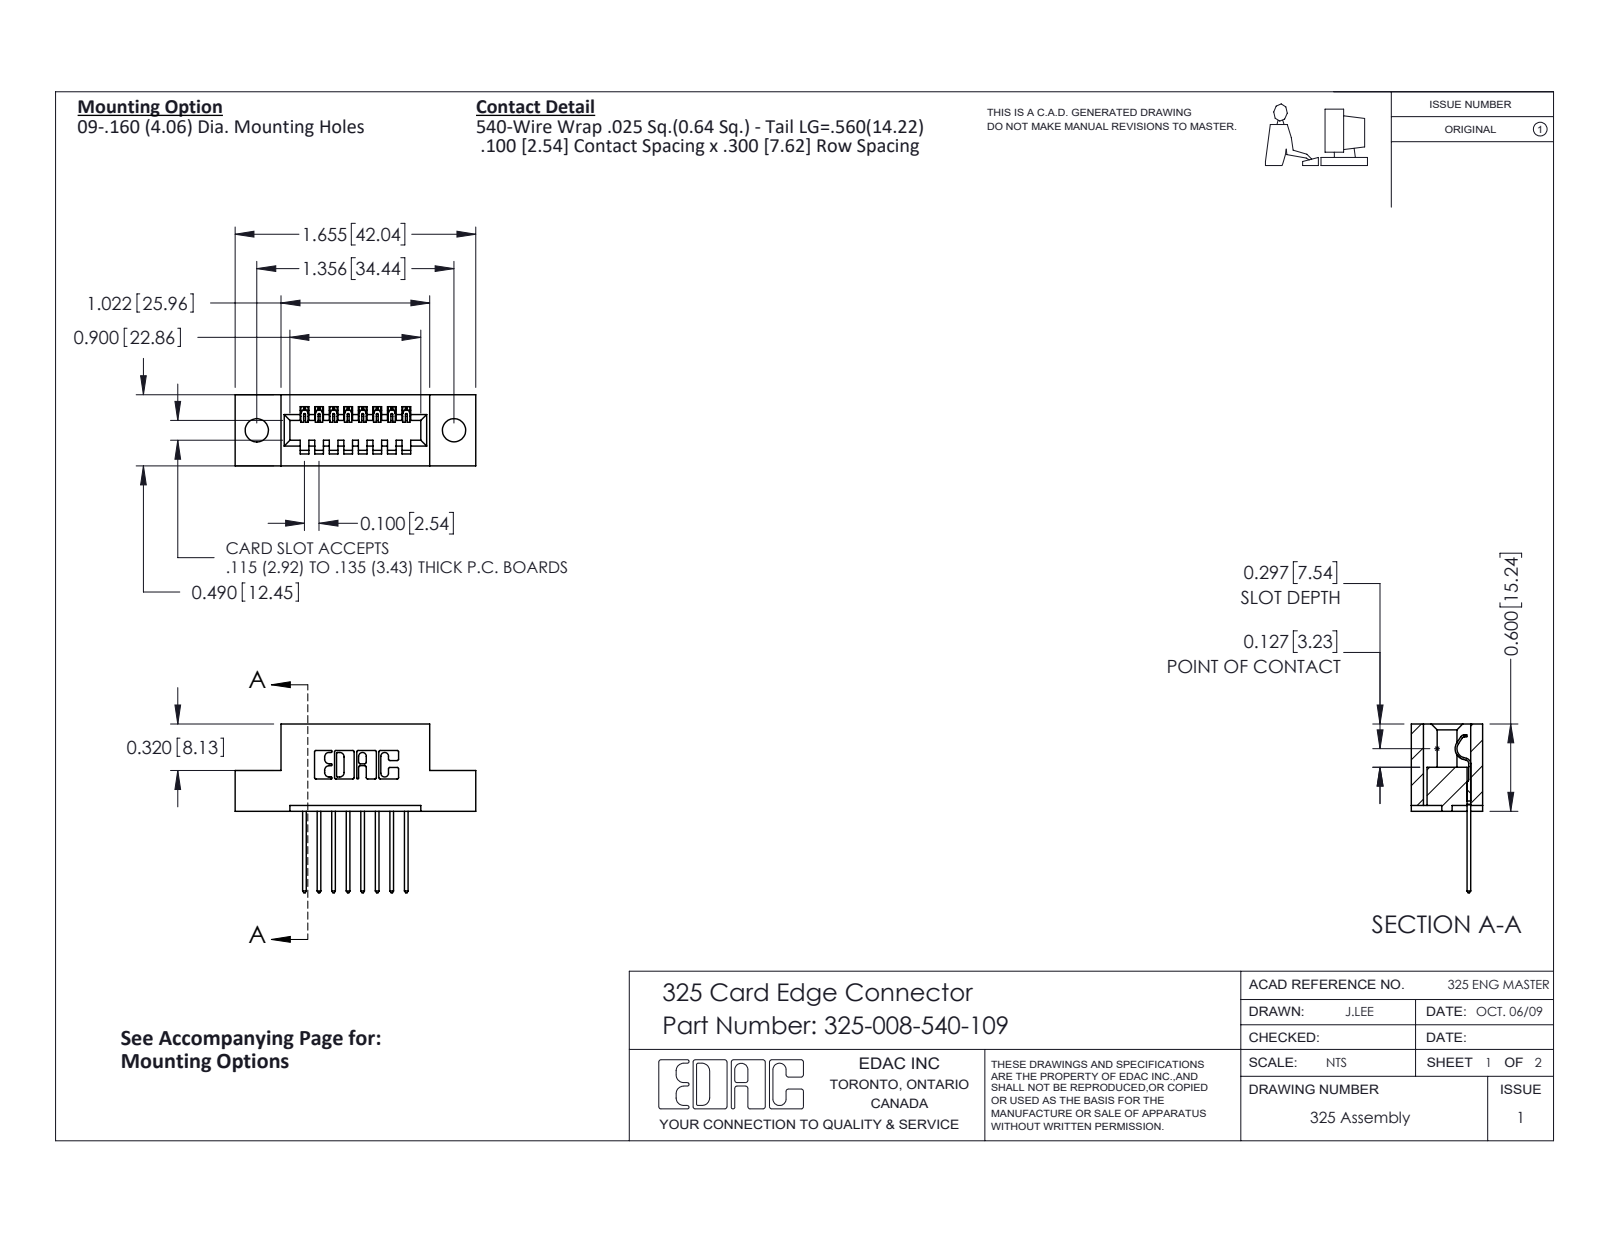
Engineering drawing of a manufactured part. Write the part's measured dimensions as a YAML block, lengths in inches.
part_name: "325 Part_.160 TH; 325-008-540-109; 325-292-001_325-293-140"
step_written_by: "SolidWorks 2016 (CONFIG_CONTROL_DESIGN)"
units: inches
bodies: {solids: 9, faces: 578, planar: 406, cylindrical: 172, other: 0}
overall_size: [1.655, 1.16, 0.49]
volume: 0.296
surface_area: 7.28
round_holes:
  - {diameter: 0.16, count: 2}
partial_cylinders:
  - {radius: 0.01, count: 22}
  - {radius: 0.006, count: 16}
  - {radius: 0.01, count: 16}
  - {radius: 0.007, count: 6}
  - {radius: 0.031, count: 6}
  - {radius: 0.026, count: 3}
  - {radius: 0.014, count: 1}
  - {radius: 0.022, count: 1}
face_to_face_distances: [0.3, 0.1, 0.2, 0.04, 0.083, 0.407, 0.49, 0.4, 0.06, 0.6]
hole_center_spacings: [1.356]
